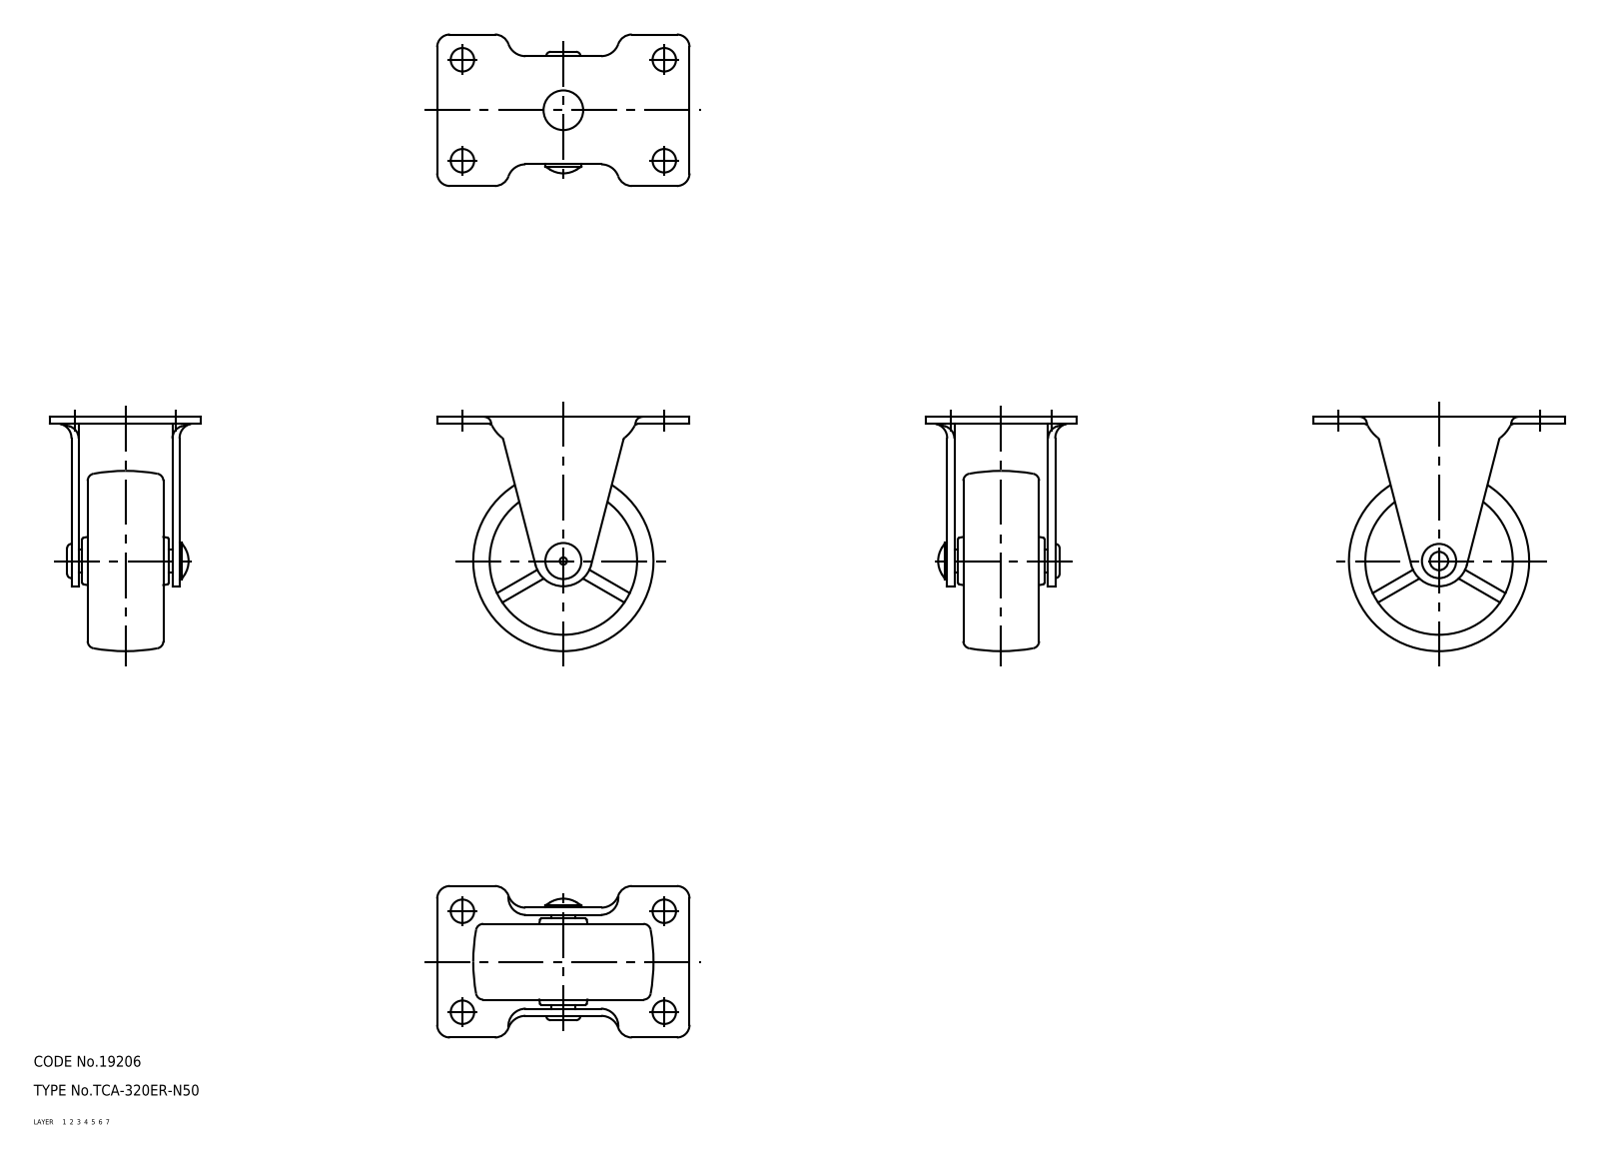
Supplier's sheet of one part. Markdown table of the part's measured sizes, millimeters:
| quantity | value |
| --- | --- |
| part name | wheel; axle; 320ER_N50_3002_36 |
| STEP written by | CADfix (AUTOMOTIVE_DESIGN) |
| units | millimeters |
| bodies | 3 solids, 241 faces (0 planar, 0 cylindrical, 241 other) |
| overall size | 70 × 65 × 42 |
| volume | 38 515 mm³ |
| surface area | 19 623 mm² |
